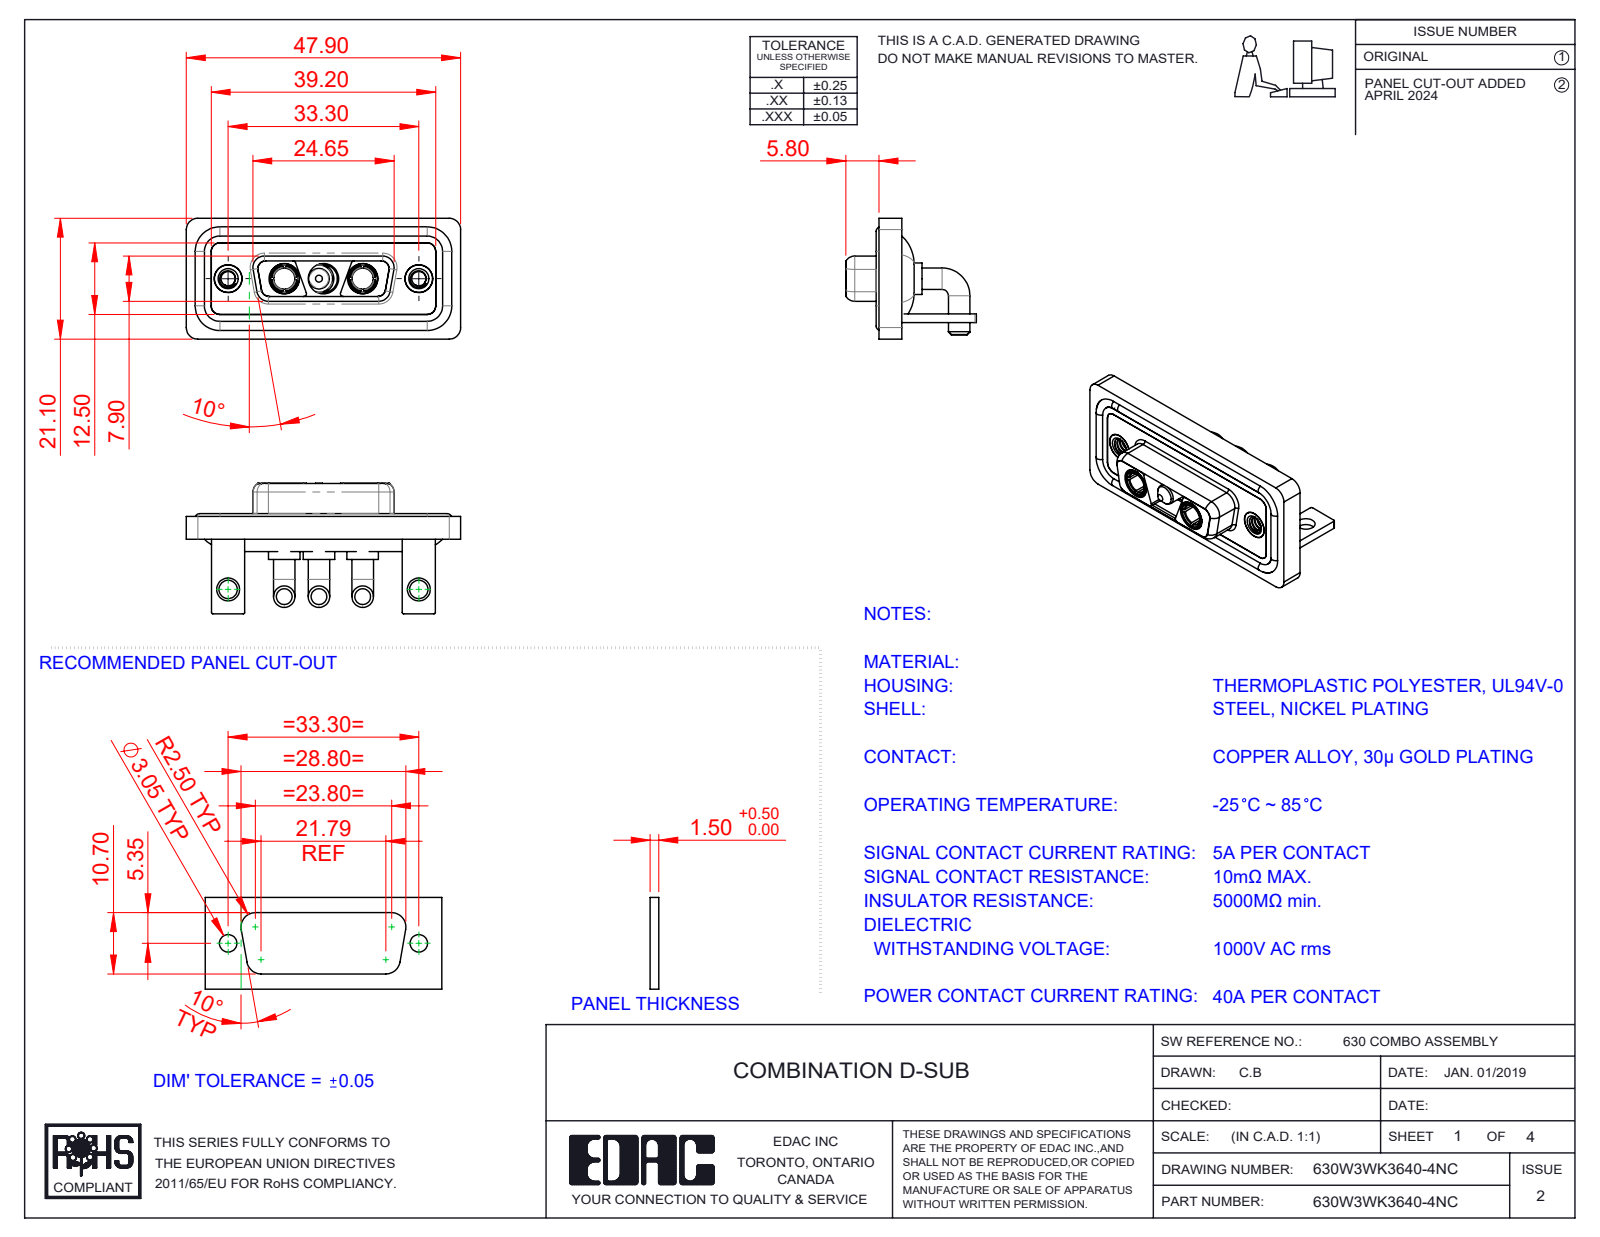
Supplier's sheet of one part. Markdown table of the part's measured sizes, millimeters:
| quantity | value |
| --- | --- |
| part name | 630Combo Threaded Rivet_A; 630Combo Housing_3WK3; Power Socket_40A RA; Power Pin_40A RA (+5 more) |
| STEP written by | SolidWorks 2023 (CONFIG_CONTROL_DESIGN) |
| units | millimeters |
| bodies | 15 solids, 637 faces (198 planar, 286 cylindrical, 153 other) |
| overall size | 47.9 × 22.8 × 21.1 |
| volume | 6 610 mm³ |
| surface area | 10 608 mm² |
| round holes (diameter × count) | 4.85 × 5, 5.3 × 3, 2.5 × 2, 3.2 × 2, 3.7 × 2, 4 × 2, 4.05 × 2, 5 × 2 |
| round bosses / shafts (diameter × count) | 3.75 × 6, 1.6 × 4, 5.5 × 3, 5.2 × 3, 4.75 × 3, 4.96 × 2, 4.95 × 2, 4.8 × 2 |
| partial cylindrical surfaces (radius × count) | 2 × 21, 1.5 × 18, 0.25 × 16, 1.35 × 12, 0.5 × 9, 1.6 × 8, 0.6 × 4, 0.65 × 4 |
| main face-to-face distances | 0.4, 2.9, 1.5, 3.7, 1.8, 1.1, 4.1, 1.6, 2.5, 1.4 |
| hole center spacings | 6.85, 9.8, 16.65, 23.5, 33.3, 13.7 |
